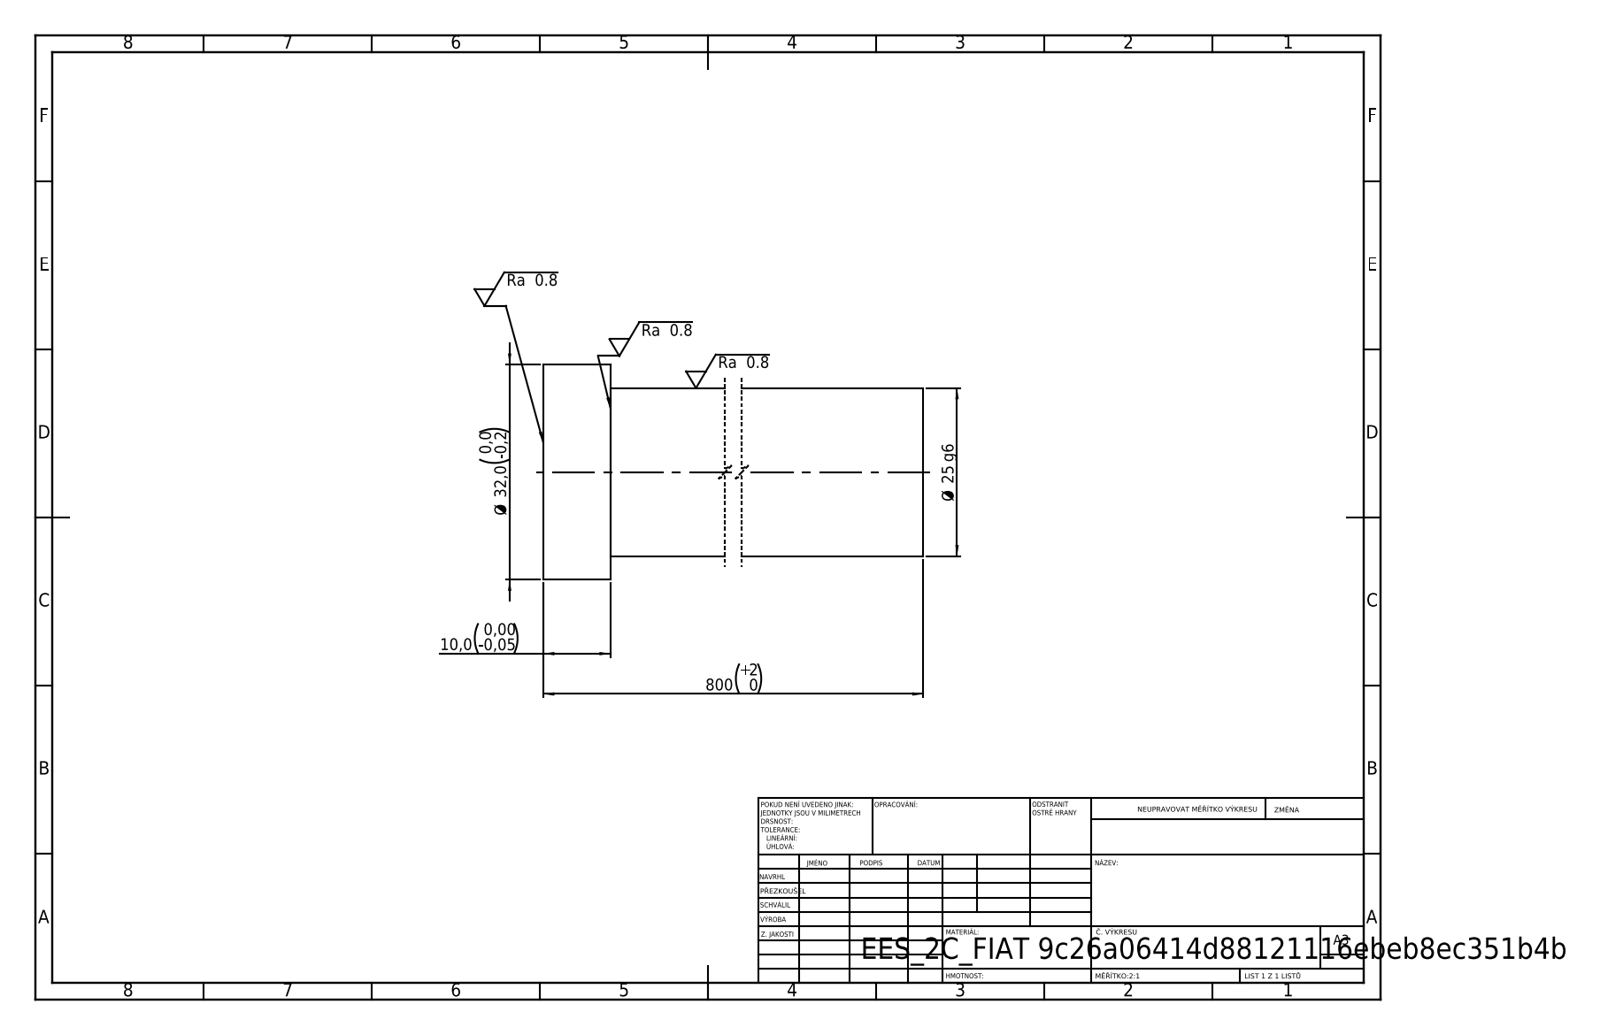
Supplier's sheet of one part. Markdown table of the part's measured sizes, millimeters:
| quantity | value |
| --- | --- |
| STEP written by | SolidWorks 2019 (CONFIG_CONTROL_DESIGN) |
| units | millimeters |
| bodies | 1 solid, 7 faces (3 planar, 4 cylindrical, 0 other) |
| overall size | 800 × 32 × 32 |
| volume | 395 833 mm³ |
| surface area | 64 660 mm² |
| round bosses / shafts (diameter × count) | 32 × 1, 25 × 1 |
| main face-to-face distances | 800, 10, 790 |
